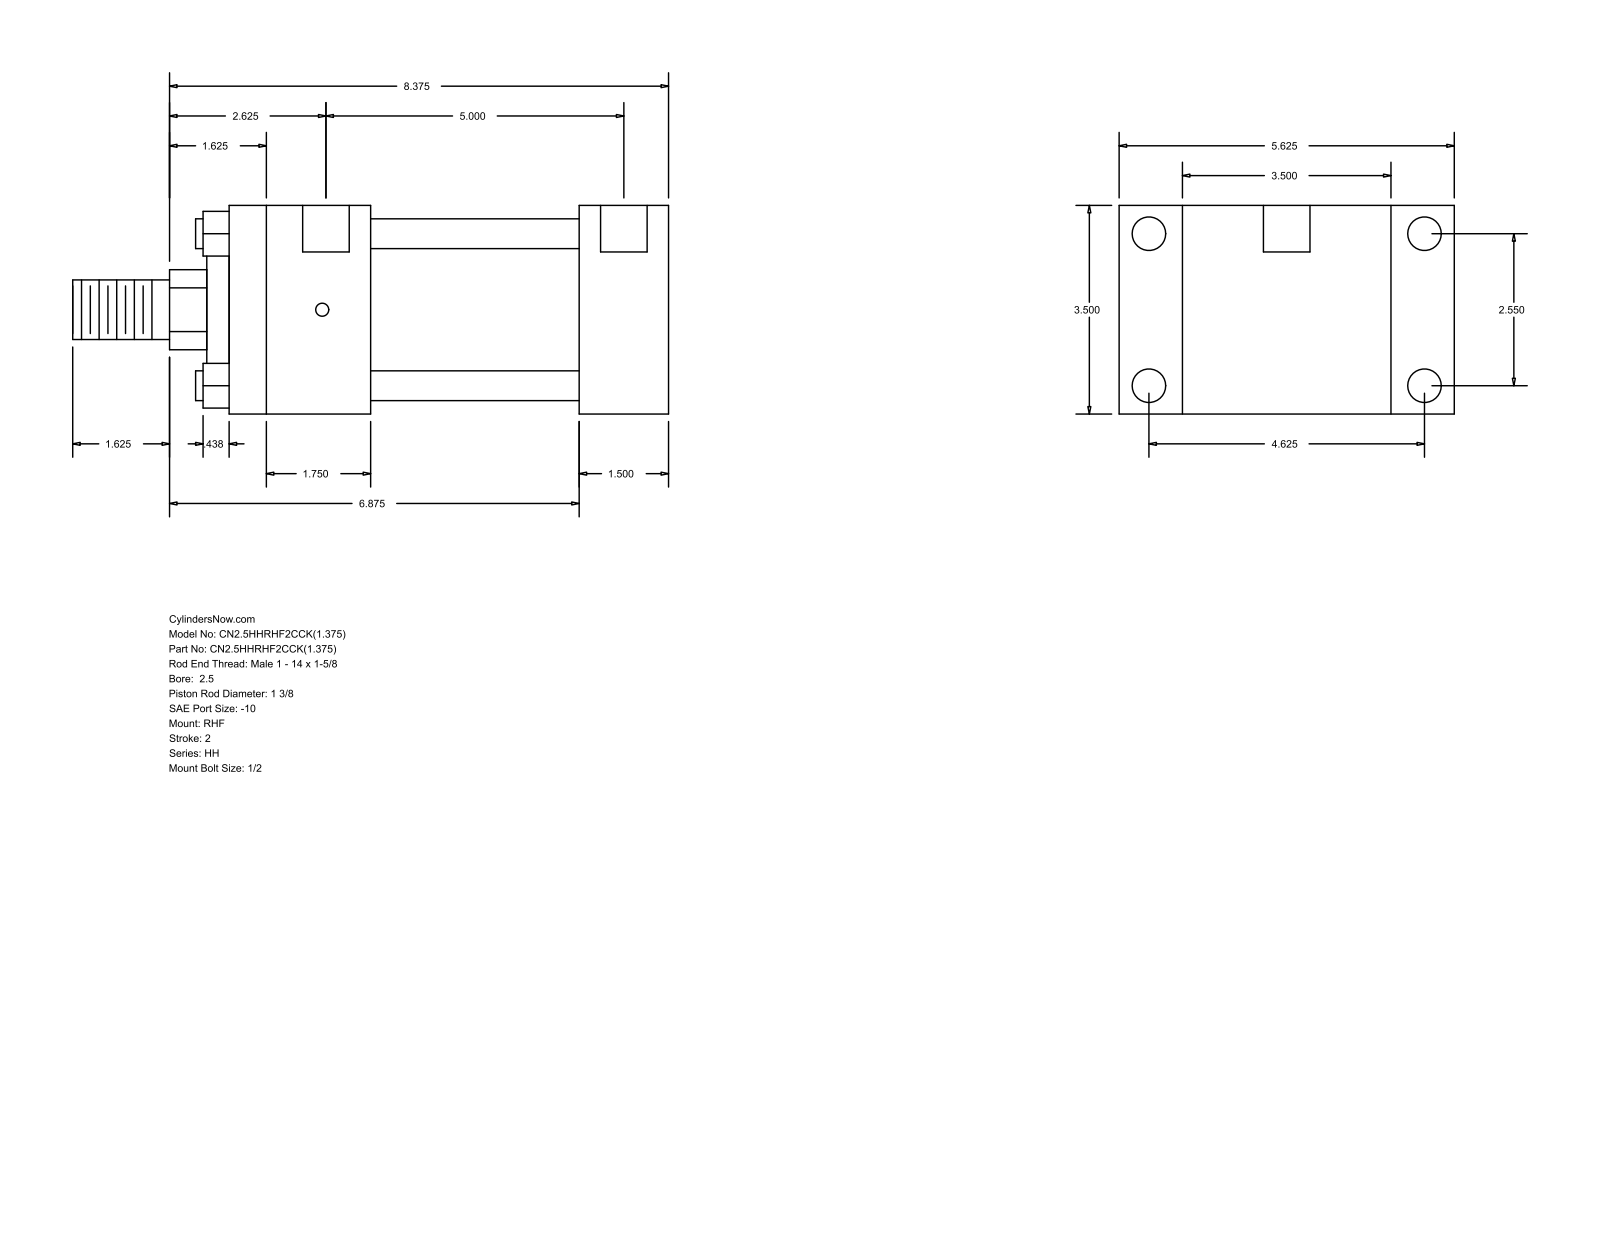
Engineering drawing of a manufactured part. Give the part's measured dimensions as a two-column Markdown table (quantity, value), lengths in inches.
| quantity | value |
| --- | --- |
| part name | HH_RHF__0250_1.375 |
| STEP written by | GSSL Pune (CONFIG_CONTROL_DESIGN) |
| units | inches |
| bodies | 0 solids, 88 faces (60 planar, 28 cylindrical, 0 other) |
| overall size | 10 × 5.625 × 3.5 |
| round holes (diameter × count) | 0.219 × 4, 0.563 × 4, 0.781 × 2 |
| round bosses / shafts (diameter × count) | 0.5 × 4, 2.875 × 1, 2 × 1, 1.375 × 1, 1 × 1 |
| partial cylindrical surfaces (radius × count) | 0.672 × 1 |
| main face-to-face distances | 3.5, 1.5, 1.063, 4.563, 5.875, 7.375, 5.625, 2.375, 5, 0.75 |
| hole center spacings | 0.062, 2.55, 4.625, 5.063, 5.125, 5.281, 5 |
